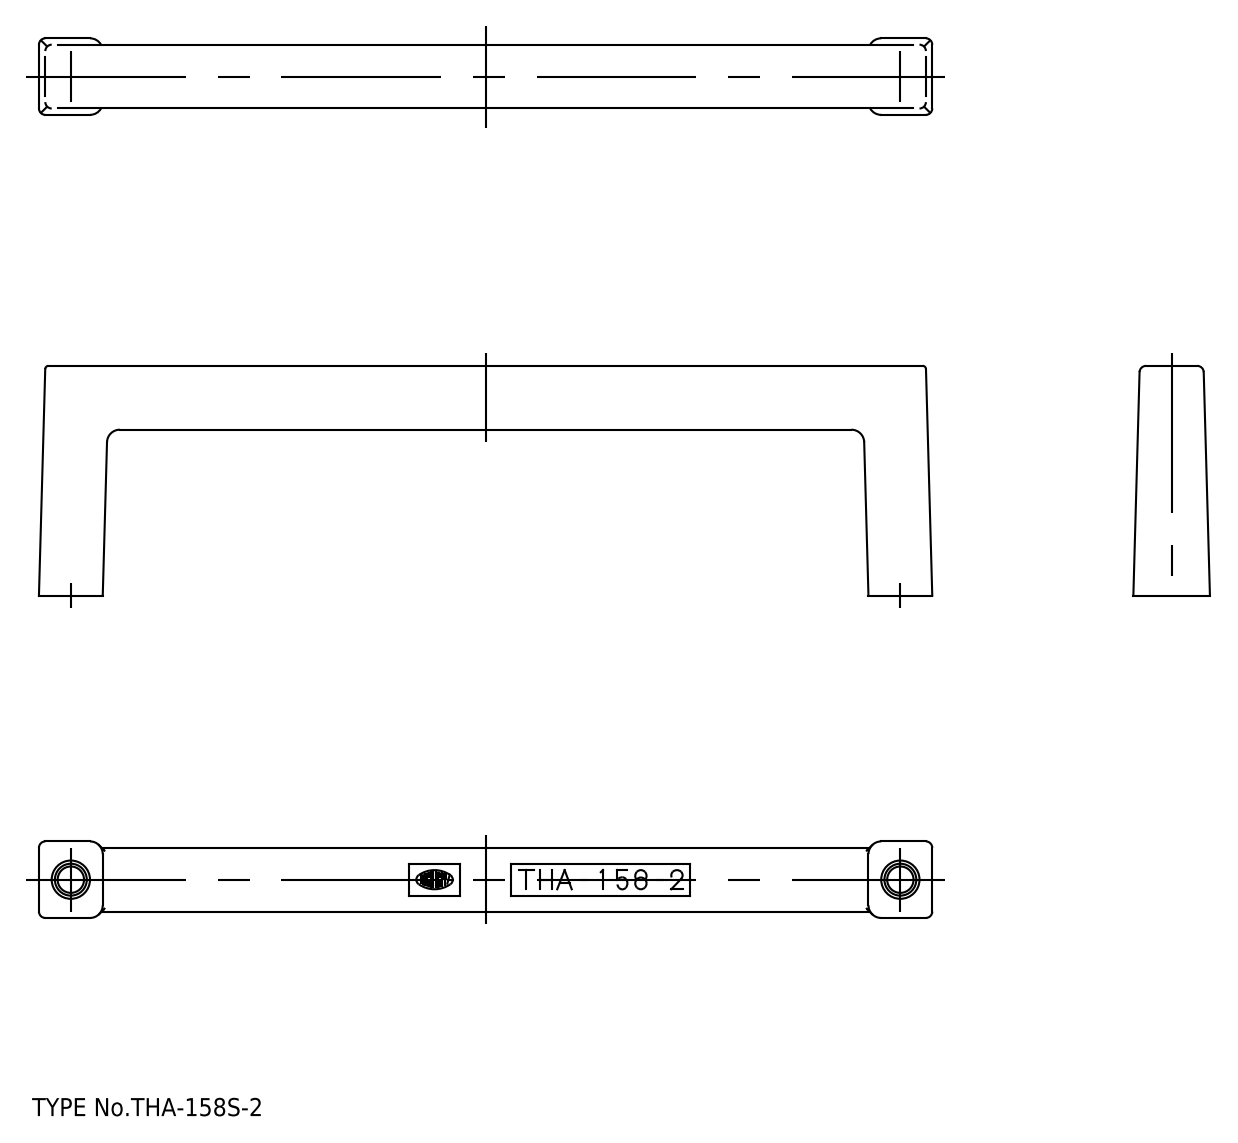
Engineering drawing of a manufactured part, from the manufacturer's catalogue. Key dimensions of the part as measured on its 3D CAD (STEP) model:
STEP written by: spGate 16.7.1 (AUTOMOTIVE_DESIGN)
Units: millimetres
Bodies: 1 solid, 44 faces (12 planar, 20 cylindrical, 12 other)
Overall size (bounding box): 140 × 36 × 12
Volume: 19 222 mm³ · Surface area: 7 924 mm²
Round holes (diameter × count): ⌀5 ×2
Partial cylindrical surfaces — rounded edges, fillets, slot ends (radius × count): R1 ×8, R2 ×8
Main face-to-face distances: 10, 36, 26, 9.99, 10.01, 24, 14, 12
Hole centre spacings: 130
